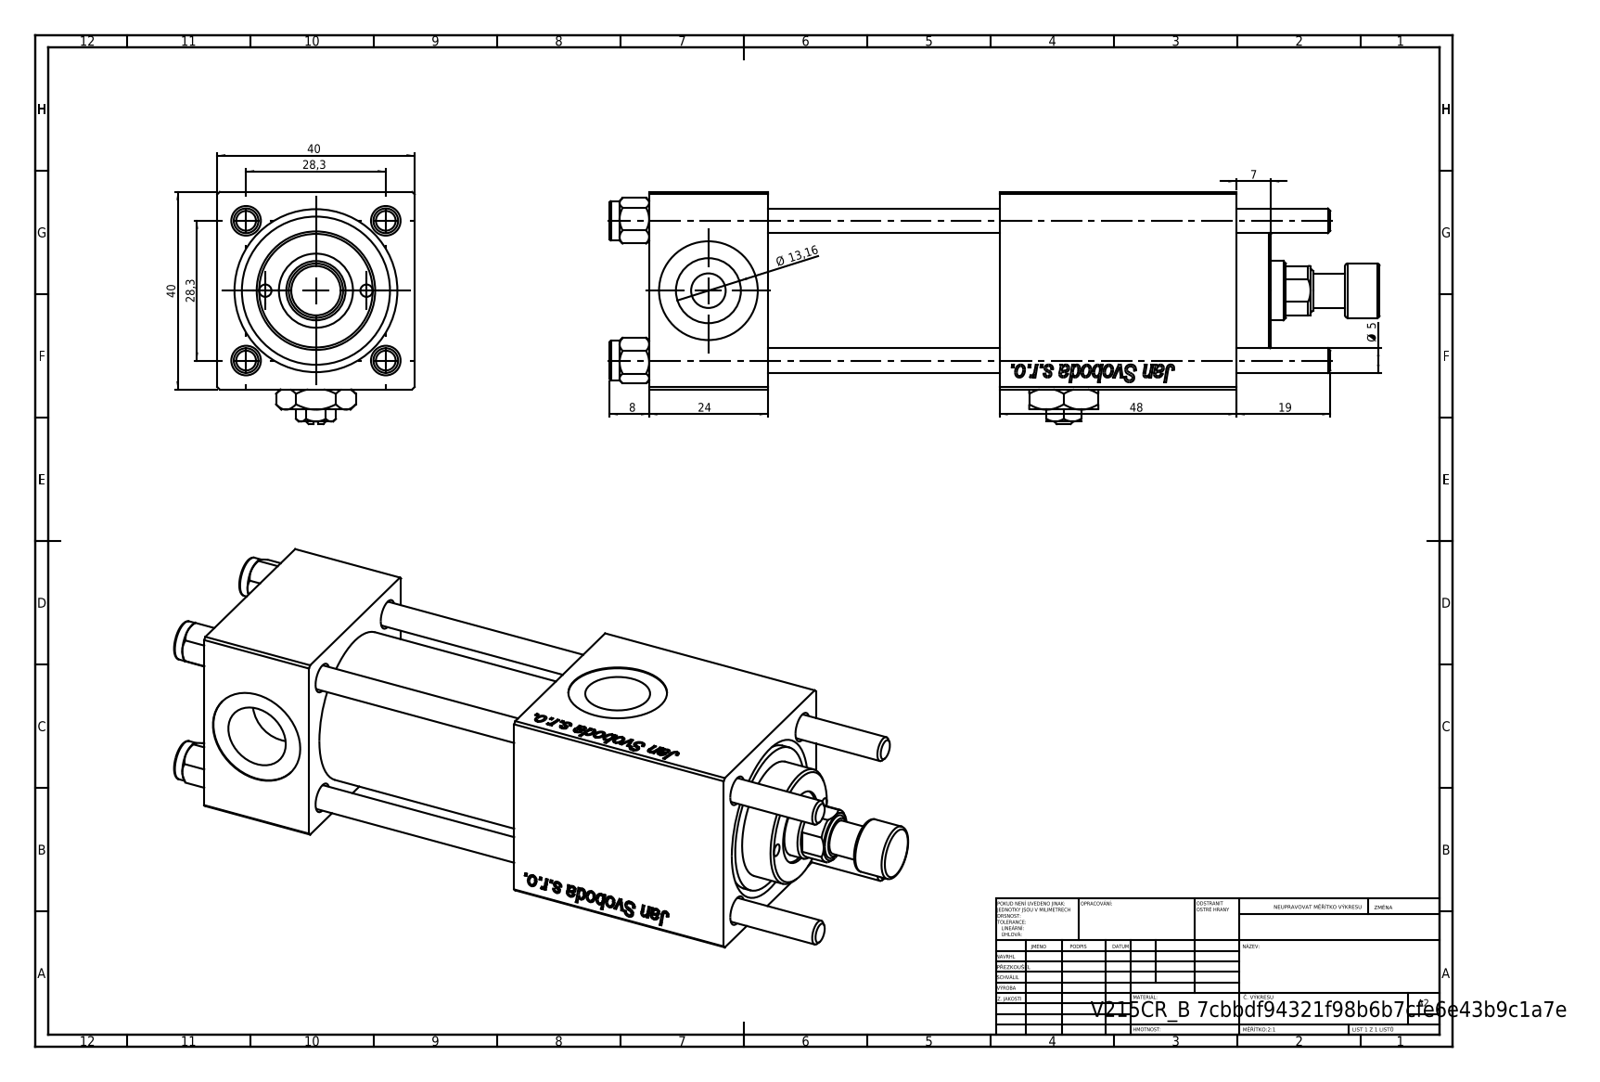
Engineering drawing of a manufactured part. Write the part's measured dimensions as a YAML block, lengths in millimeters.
part_name: "V215CR_B_TYCINKA; V215_VC_A; V215CR_ROD_END_F; Zatka_pro_OIL_PORT (+3 more)"
step_written_by: "SolidWorks 2019 (CONFIG_CONTROL_DESIGN)"
units: millimeters
bodies: {solids: 13, faces: 1223, planar: 459, cylindrical: 90, other: 674}
overall_size: [156, 47, 40]
volume: 145059
surface_area: 60157
round_holes:
  - {diameter: 5, count: 4}
  - {diameter: 20, count: 4}
  - {diameter: 13.16, count: 3}
  - {diameter: 2.5, count: 2}
  - {diameter: 7, count: 2}
  - {diameter: 6.5, count: 1}
  - {diameter: 12, count: 1}
  - {diameter: 15, count: 1}
  - {diameter: 25, count: 1}
  - {diameter: 30, count: 1}
round_bosses_or_shafts:
  - {diameter: 8, count: 4}
  - {diameter: 31, count: 1}
  - {diameter: 24, count: 1}
  - {diameter: 11, count: 1}
face_to_face_distances: [40, 24, 47, 90.3, 66.3, 71, 19.3, 119, 95, 48]
hole_center_spacings: [14.68, 20.01, 28.21, 28.3, 10.25, 40.02, 20.5]
